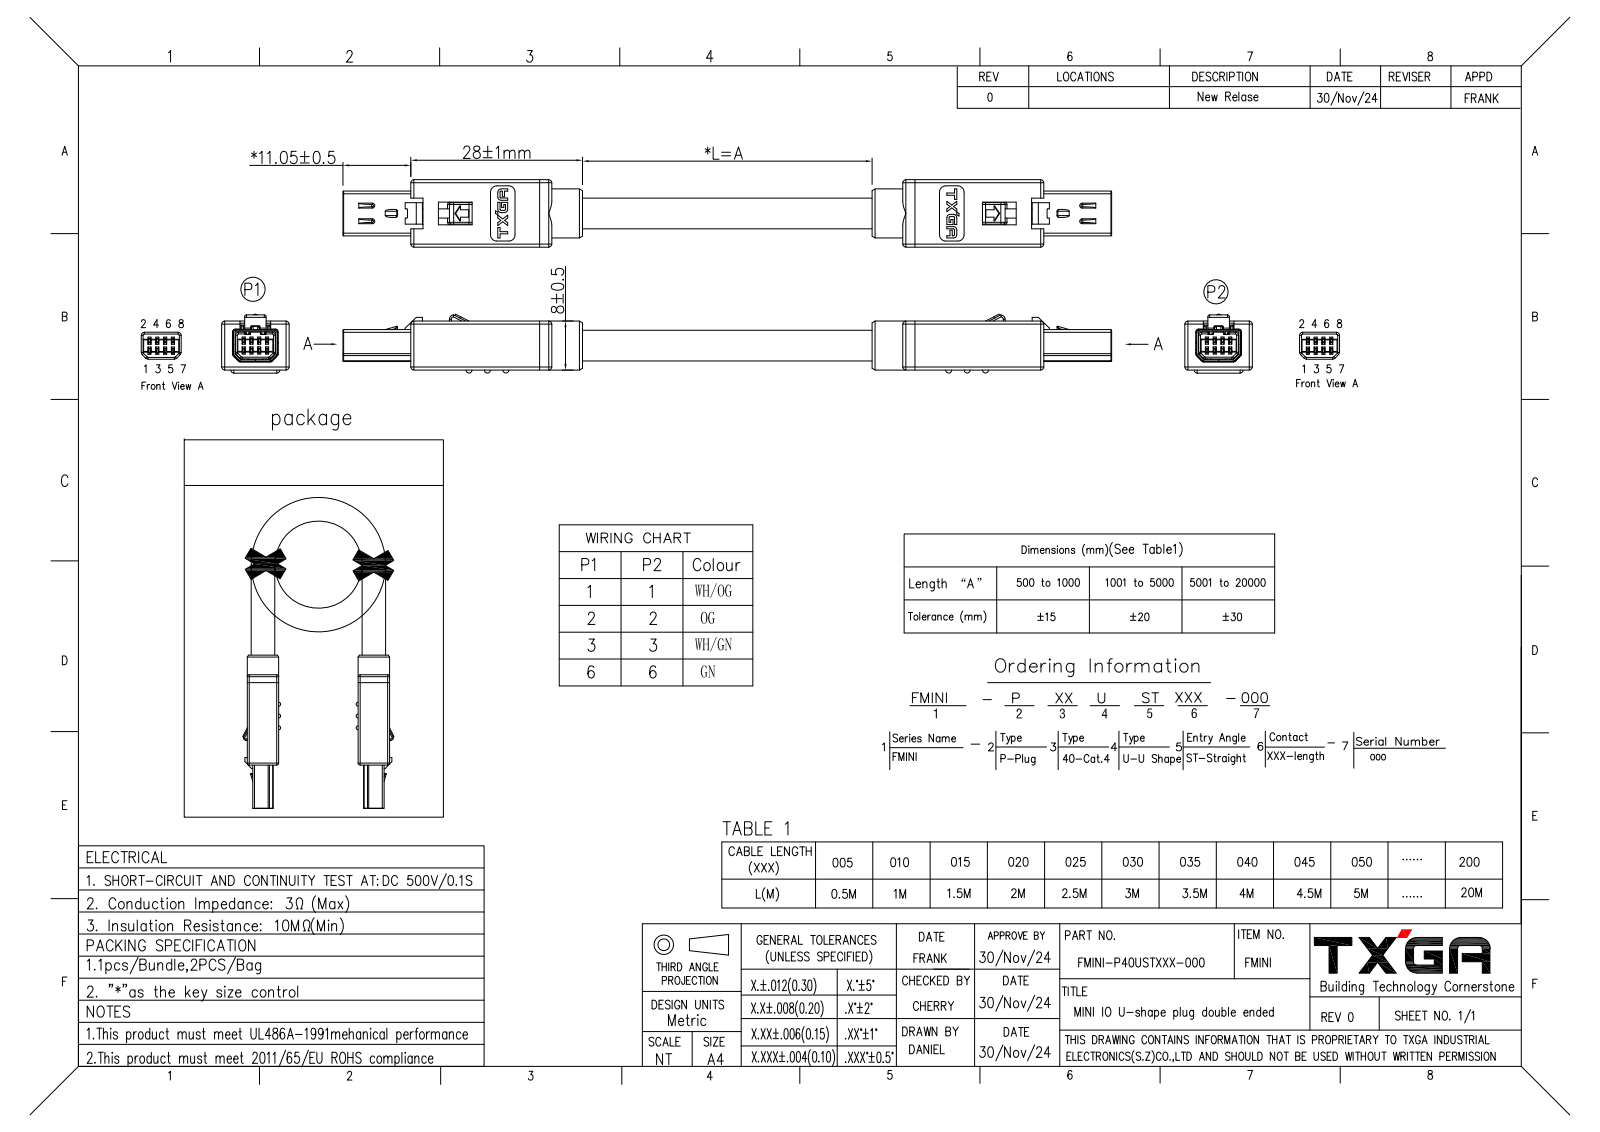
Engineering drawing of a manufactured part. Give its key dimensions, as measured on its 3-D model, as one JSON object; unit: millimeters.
{"part_name": "FMINI-PUSTXXX-000", "step_written_by": "PRO/ENGINEER BY PARAMETRIC TECHNOLOGY CORPORATION, 2010280 (CONFIG_CONTROL_DESIGN)", "units": "millimeters", "bodies": {"solids": 1, "faces": 4522, "planar": 3022, "cylindrical": 1128, "other": 372}, "overall_size": [110.1, 11, 9.62], "volume_mm3": 4847, "surface_area_mm2": 9203, "round_bosses_or_shafts": [[8, 1], [6, 1]], "partial_cylinders_radius": [[0.2, 112], [0.1, 70], [0.3, 62], [0.5, 54], [0.8, 40], [0.45, 30], [1, 16], [0.15, 11]], "face_to_face_distances": [0.35, 0.65, 1.4, 1.75, 1, 0.75, 4.85, 0.5, 6.25, 6.6]}
